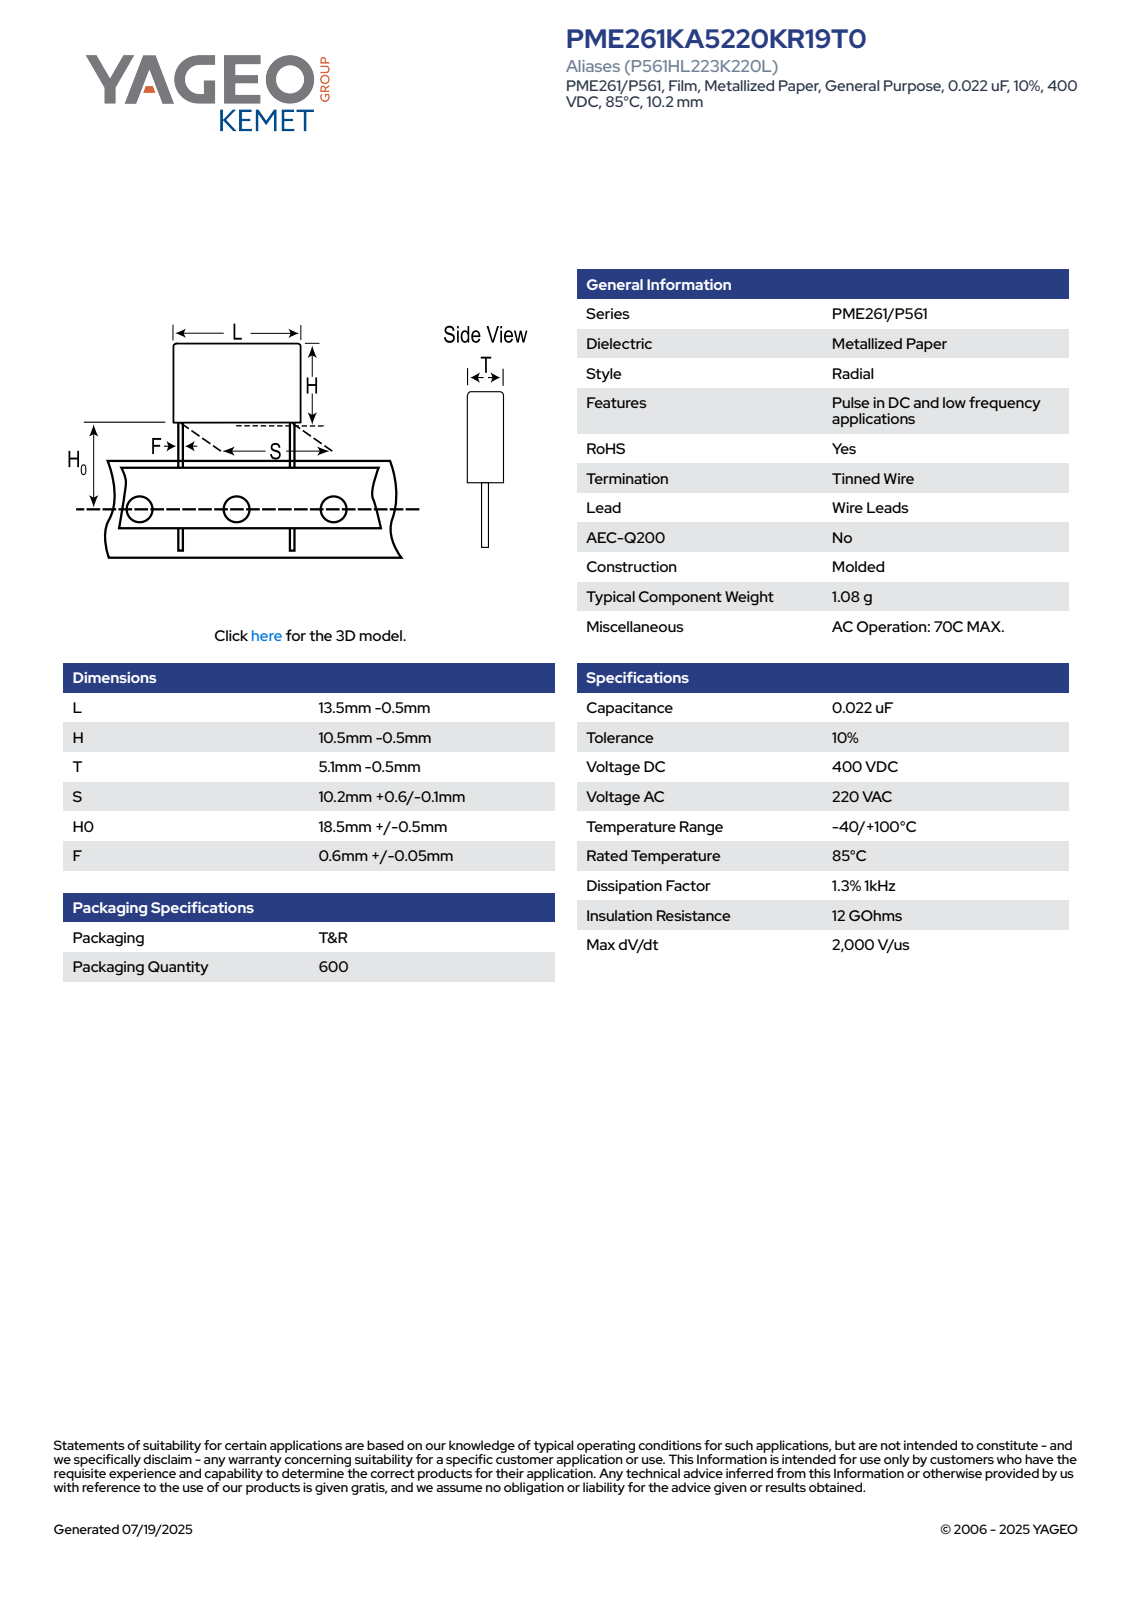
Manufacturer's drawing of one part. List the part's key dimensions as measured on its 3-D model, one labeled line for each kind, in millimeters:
Part name (STEP PRODUCT): CFR_MOLDED_13.5X10.5X5.1_L13H10T4.6S10.2H019F0.65
STEP written by: SolidWorks 2014 (AUTOMOTIVE_DESIGN)
Units: millimetres
Bodies: 4 solids, 73 faces (65 planar, 8 cylindrical, 0 other)
Overall size (bounding box): 29 × 13 × 4.61
Volume: 609 mm³ · Surface area: 550 mm²
Round bosses / shafts (diameter × count): ⌀0.65 ×2
Partial cylindrical surfaces — rounded edges, fillets, slot ends (radius × count): R0.5 ×4
Main face-to-face distances: 4.6, 13, 10, 19, 29, 1.17, 24.36, 5.36, 4.64, 23.19
